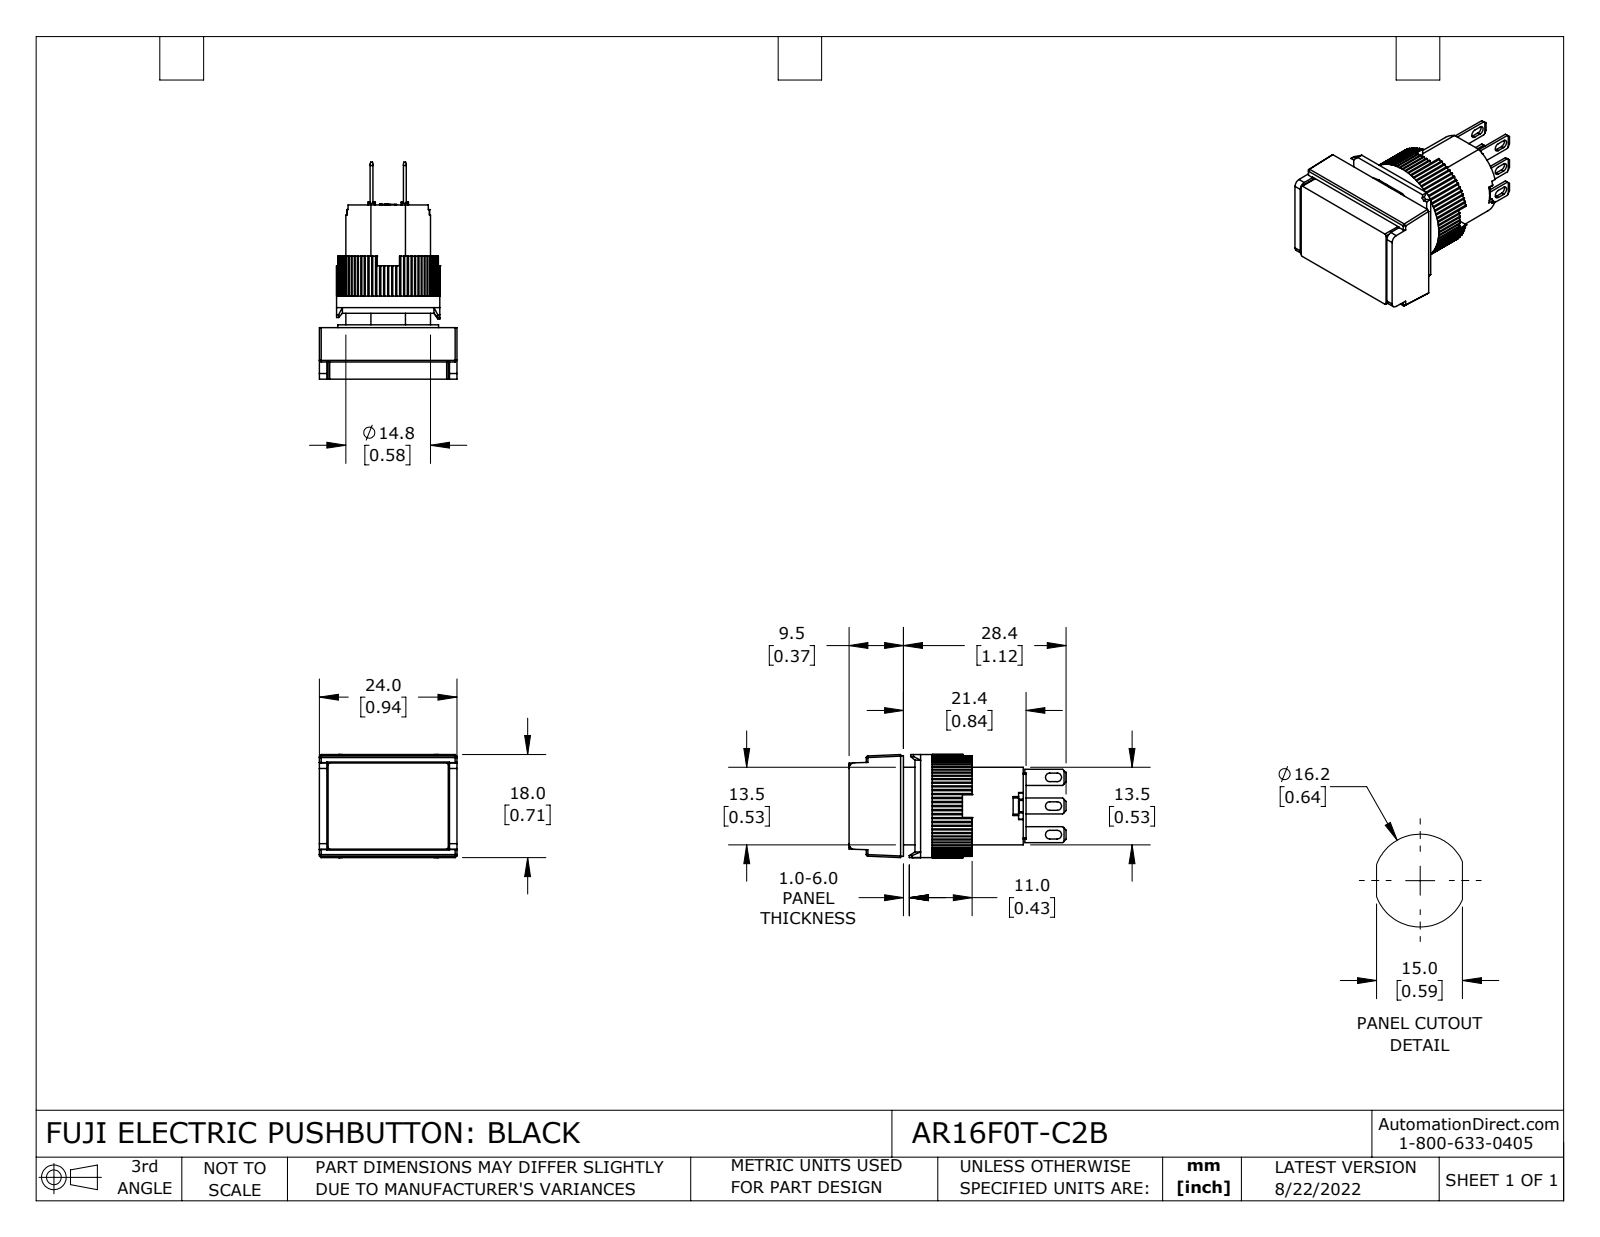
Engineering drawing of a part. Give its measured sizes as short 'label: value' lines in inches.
name: AR16F0T-C2B
written by: SolidWorks 2021 (CONFIG_CONTROL_DESIGN)
unit: in
bodies: 12 solids, 813 faces (632 planar, 177 cylindrical, 4 other)
size: 1.492 × 0.945 × 0.709
volume: 0.443 in³; area: 9.124 in²
holes: 1× ⌀0.543, 1× ⌀0.583
bosses: 1× ⌀0.709, 1× ⌀0.693
rounds: 80× R0.01, 12× R0.008, 6× R0.012, 6× R0.03, 2× R0.039
face distances: 0.213, 0.354, 0.142, 0.492, 0.35, 0.138, 0.02, 0.843, 0.059, 0.453
